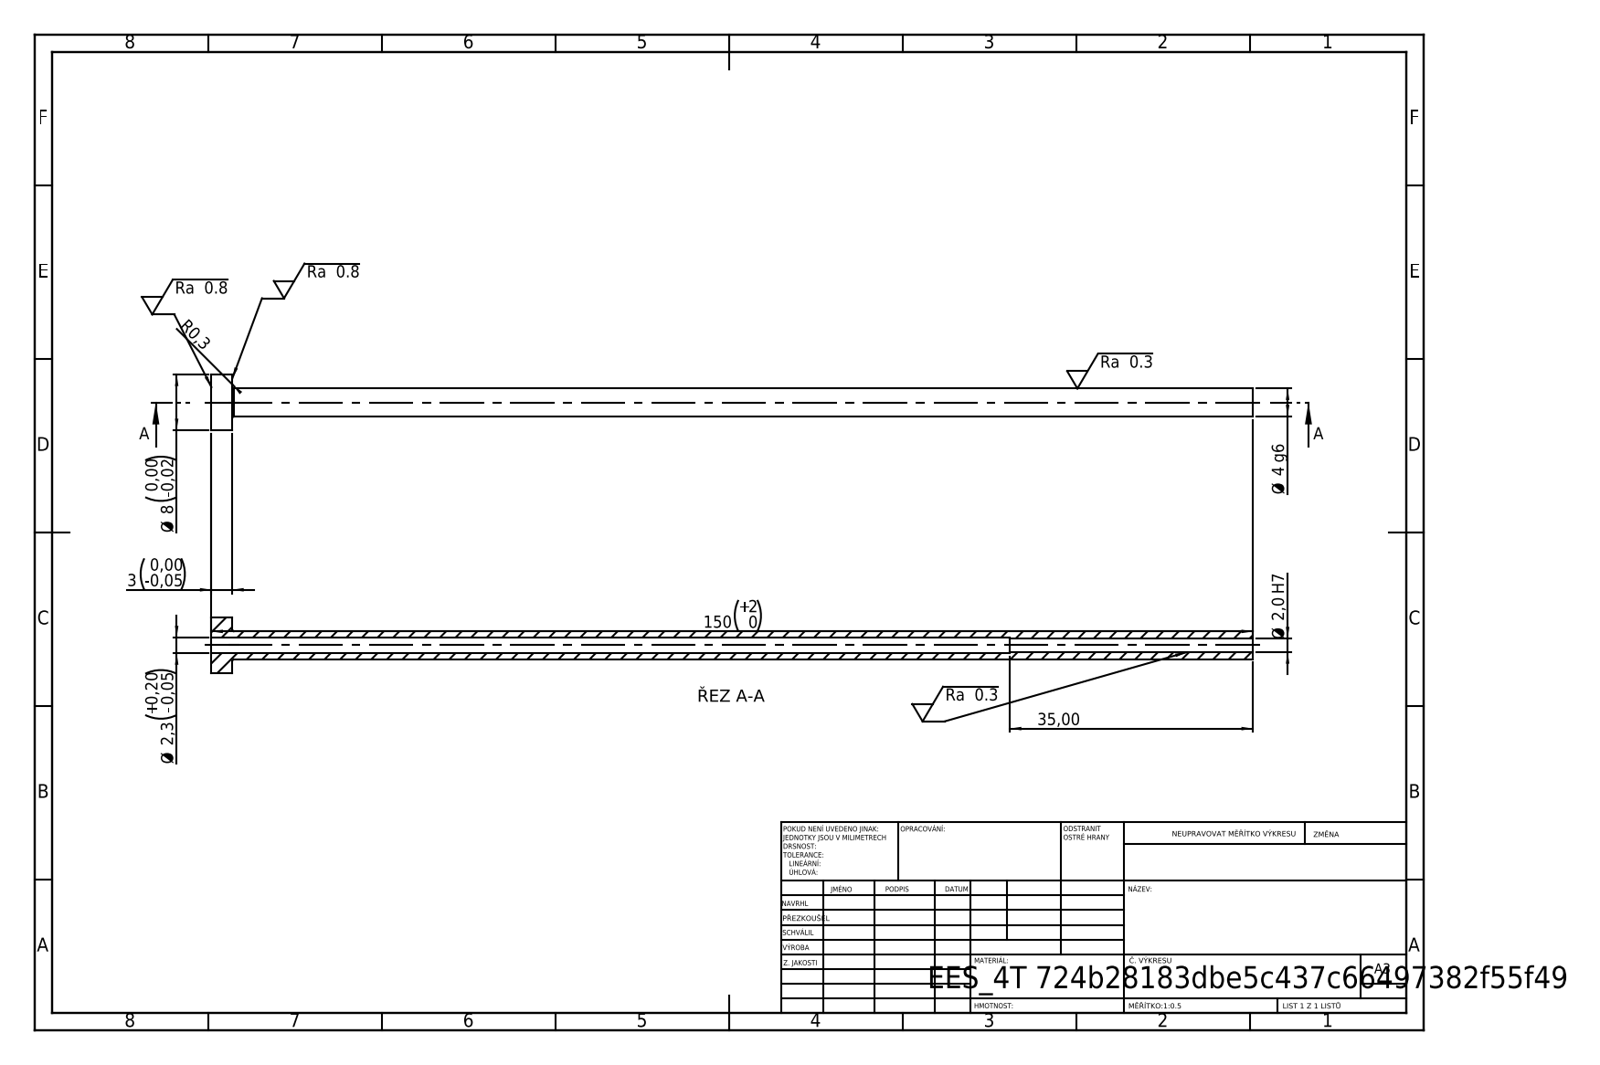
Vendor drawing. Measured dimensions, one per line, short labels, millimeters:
written by: SolidWorks 2019 (CONFIG_CONTROL_DESIGN)
unit: mm
bodies: 1 solid, 14 faces (4 planar, 8 cylindrical, 2 other)
size: 150 × 8 × 8
volume: 1 411 mm³; area: 3 066 mm²
holes: 1× ⌀2, 1× ⌀2.3
bosses: 1× ⌀8, 1× ⌀4
face distances: 3, 150, 147, 115, 112, 35
